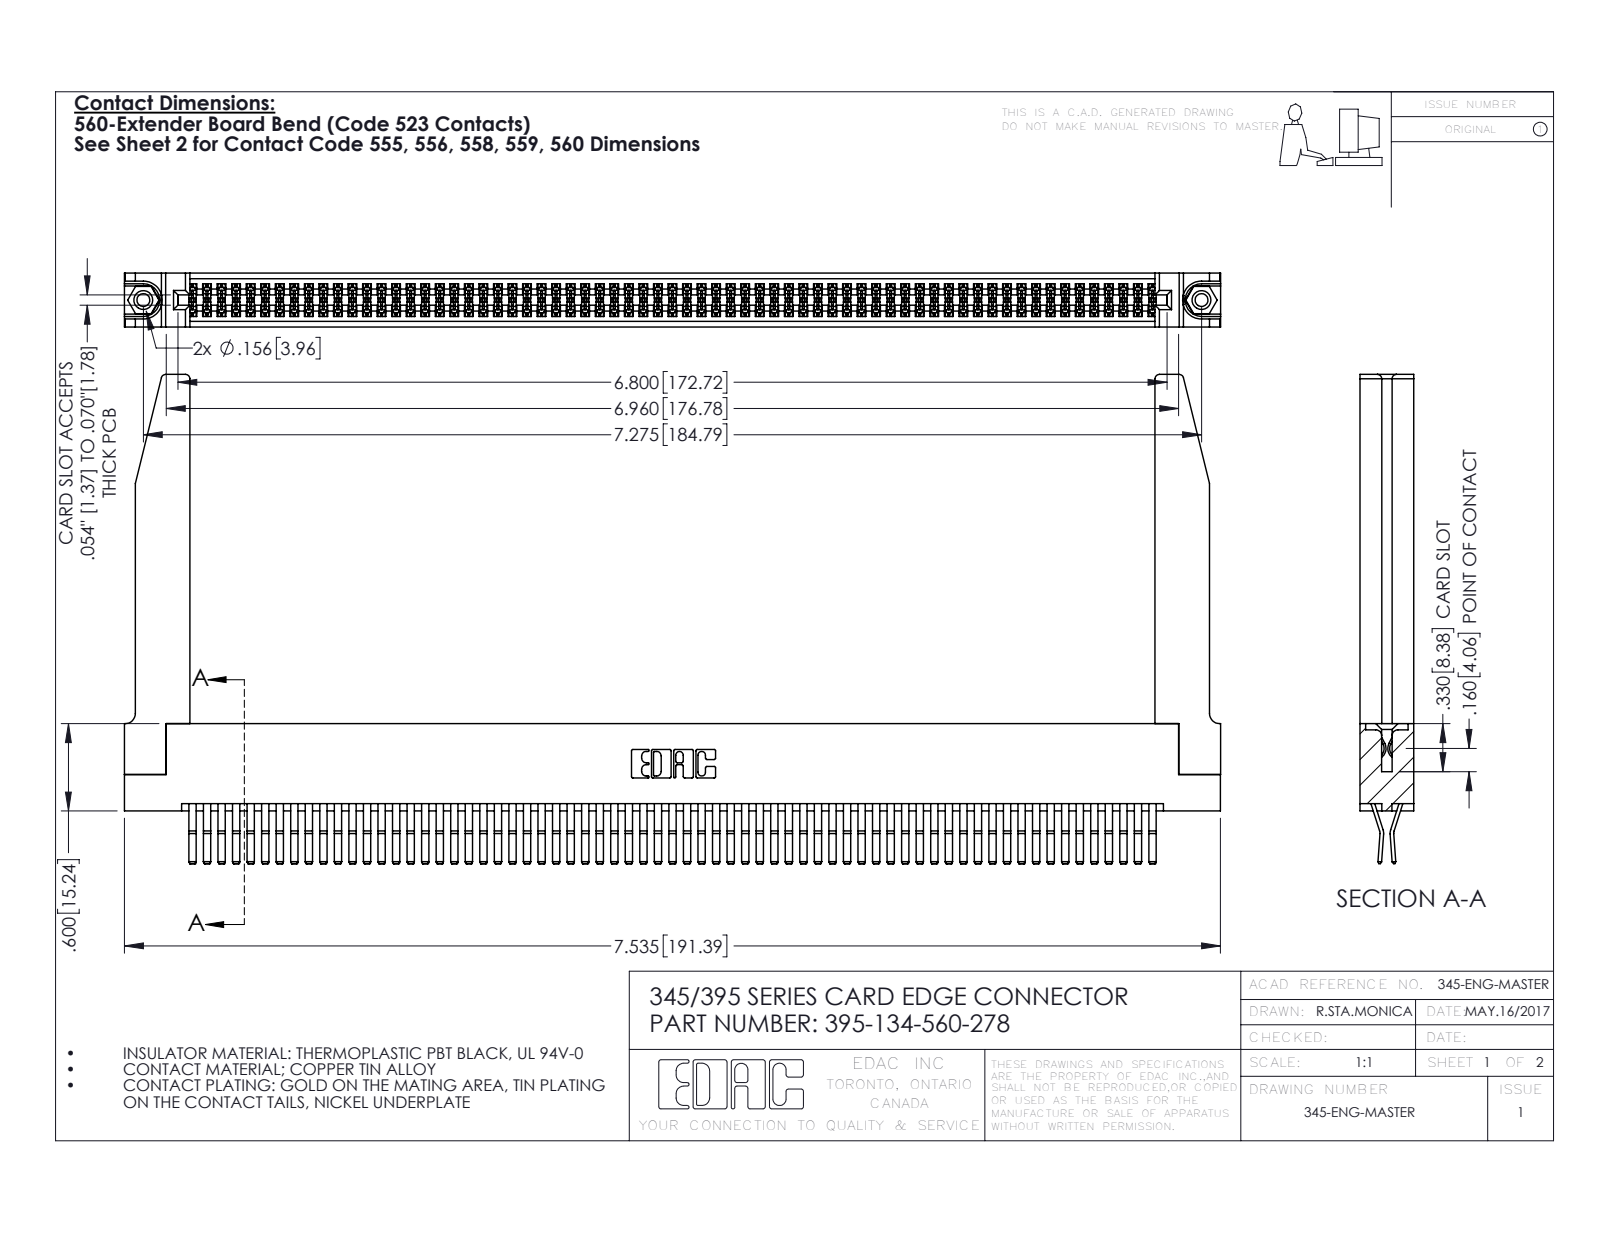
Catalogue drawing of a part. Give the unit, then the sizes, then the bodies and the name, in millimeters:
Units: millimetres
Overall size (bounding box): 191.4 × 85.4 × 9.4
Round holes (diameter × count): ⌀2.3 ×2, ⌀3.2 ×2, ⌀4 ×2, ⌀1.6 ×1
Round bosses / shafts (diameter × count): ⌀3.9 ×2
Partial cylindrical surfaces — rounded edges, fillets, slot ends (radius × count): R0.2 ×201, R0.3 ×22, R0.8 ×8, R0.2 ×6, R0.8 ×6, R0.7 ×3, R0.3 ×2, R0.4 ×2
Main face-to-face distances: 1.8, 0.6, 7.6, 9.4, 5.1, 2.5, 6.9, 5.7, 4.4, 3.8
Hole centre spacings: 6.9, 178.8, 184.8
Volume: 27 480 mm³ · Surface area: 38 710 mm²
Bodies: 139 solids, 7328 faces (4644 planar, 2632 cylindrical, 52 other)
Part name (STEP PRODUCT): 345 Part_Flush Mounting Lugs - 0.156 Dia-TH; 345-292-001_560 Tail; 345-220-078_345-220-078; 345-250-001_345-250-001-102 (+1 more)
STEP written by: SolidWorks 2016 (CONFIG_CONTROL_DESIGN)
